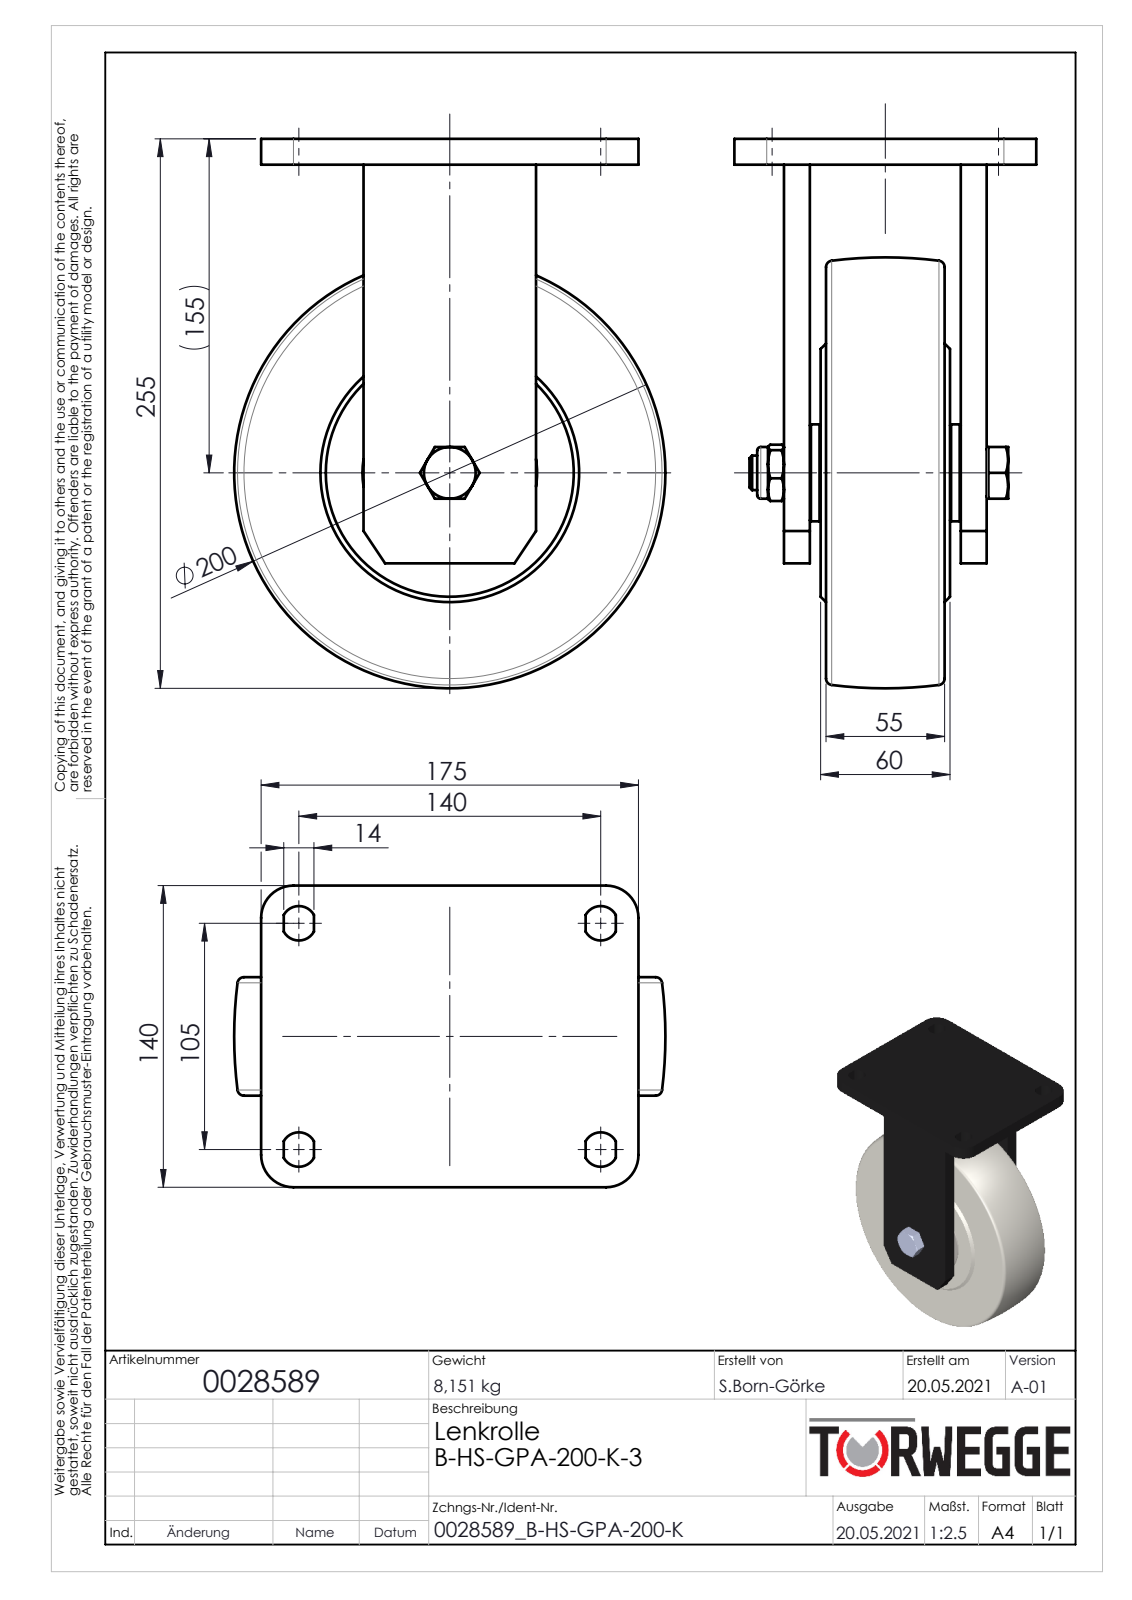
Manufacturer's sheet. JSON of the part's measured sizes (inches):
{"part_name": "0028589", "step_written_by": "SolidWorks 2020 (AUTOMOTIVE_DESIGN)", "units": "inches", "bodies": {"solids": 17, "faces": 293, "planar": 85, "cylindrical": 108, "other": 100}, "overall_size": [10.039, 7.874, 5.512], "volume_in3": 143, "surface_area_in2": 508.8, "round_holes": [[0.551, 1], [0.63, 1], [0.642, 1], [0.72, 1], [1.378, 1], [1.417, 1], [1.848, 1], [2.572, 1], [2.68, 1], [2.835, 1], [3.15, 1]], "round_bosses_or_shafts": [[1.956, 1], [1.772, 1], [0.945, 1]], "partial_cylinders_radius": [[0.315, 4], [0.591, 4]], "face_to_face_distances": [0.472, 0.295, 2.461, 0.768, 2.933, 3.228, 0.669, 3.031, 0.197, 2.559]}
